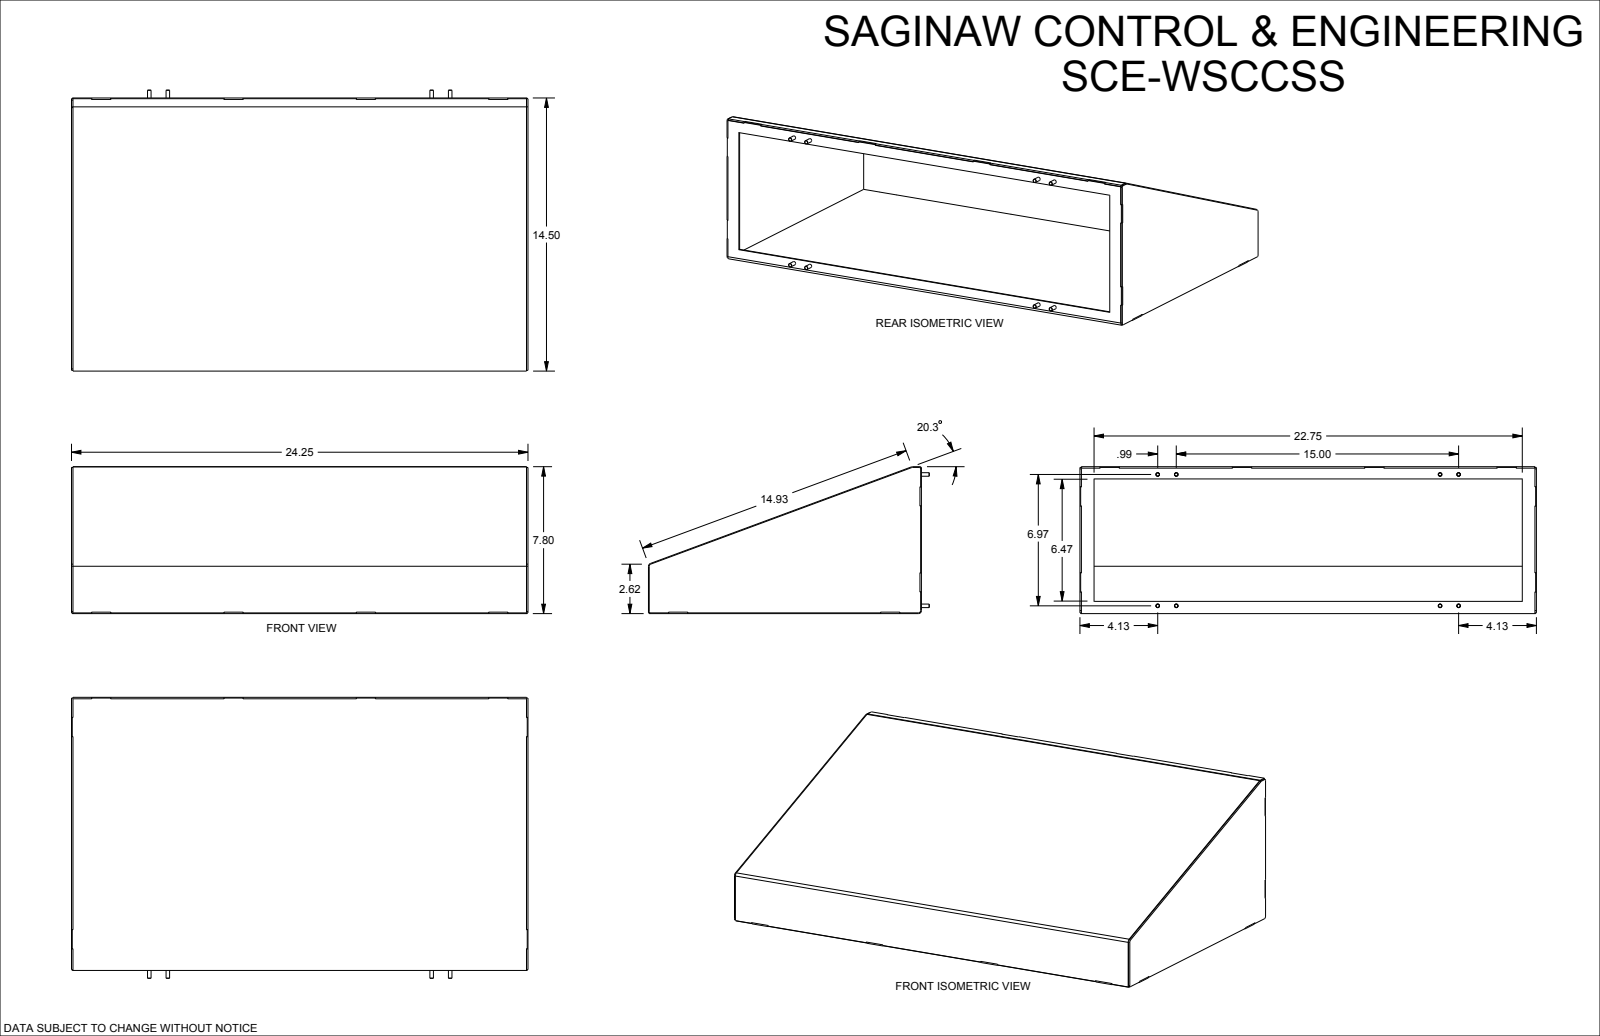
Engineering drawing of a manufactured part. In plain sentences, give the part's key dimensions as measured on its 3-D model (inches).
The part is named "SCE-WSCC". Its 3-D file was written by "SolidWorks 2019 (AUTOMOTIVE_DESIGN)". It is 12 solids with 254 faces: 188 planar, 58 cylindrical and 8 other. Overall it measures 24.25 by 14.912 by 7.8 inches. Its volume is 75.25 cubic inches and its surface area 1 955 square inches. Round holes: 8 of diameter 0.193, 4 of diameter 0.22, 1 of diameter 0.44. Round bosses or shafts: 8 of diameter 0.26, 8 of diameter 0.19. Partial cylindrical surfaces (rounded edges, fillets, slot ends): 12 of radius 0.015, 3 of radius 0.08, 3 of radius 0.12, 3 of radius 0.158, 2 of radius 0.078. The main face-to-face distances are 0.078, 24.172, 24.094, 24.25, 14.422, 14.344, 14.5, 7.722, 0.039, 7.644. The hole center spacings are 0.985, 6.974, 7.043, 7.203, 7.743, 15, 16.542, 3.677.
